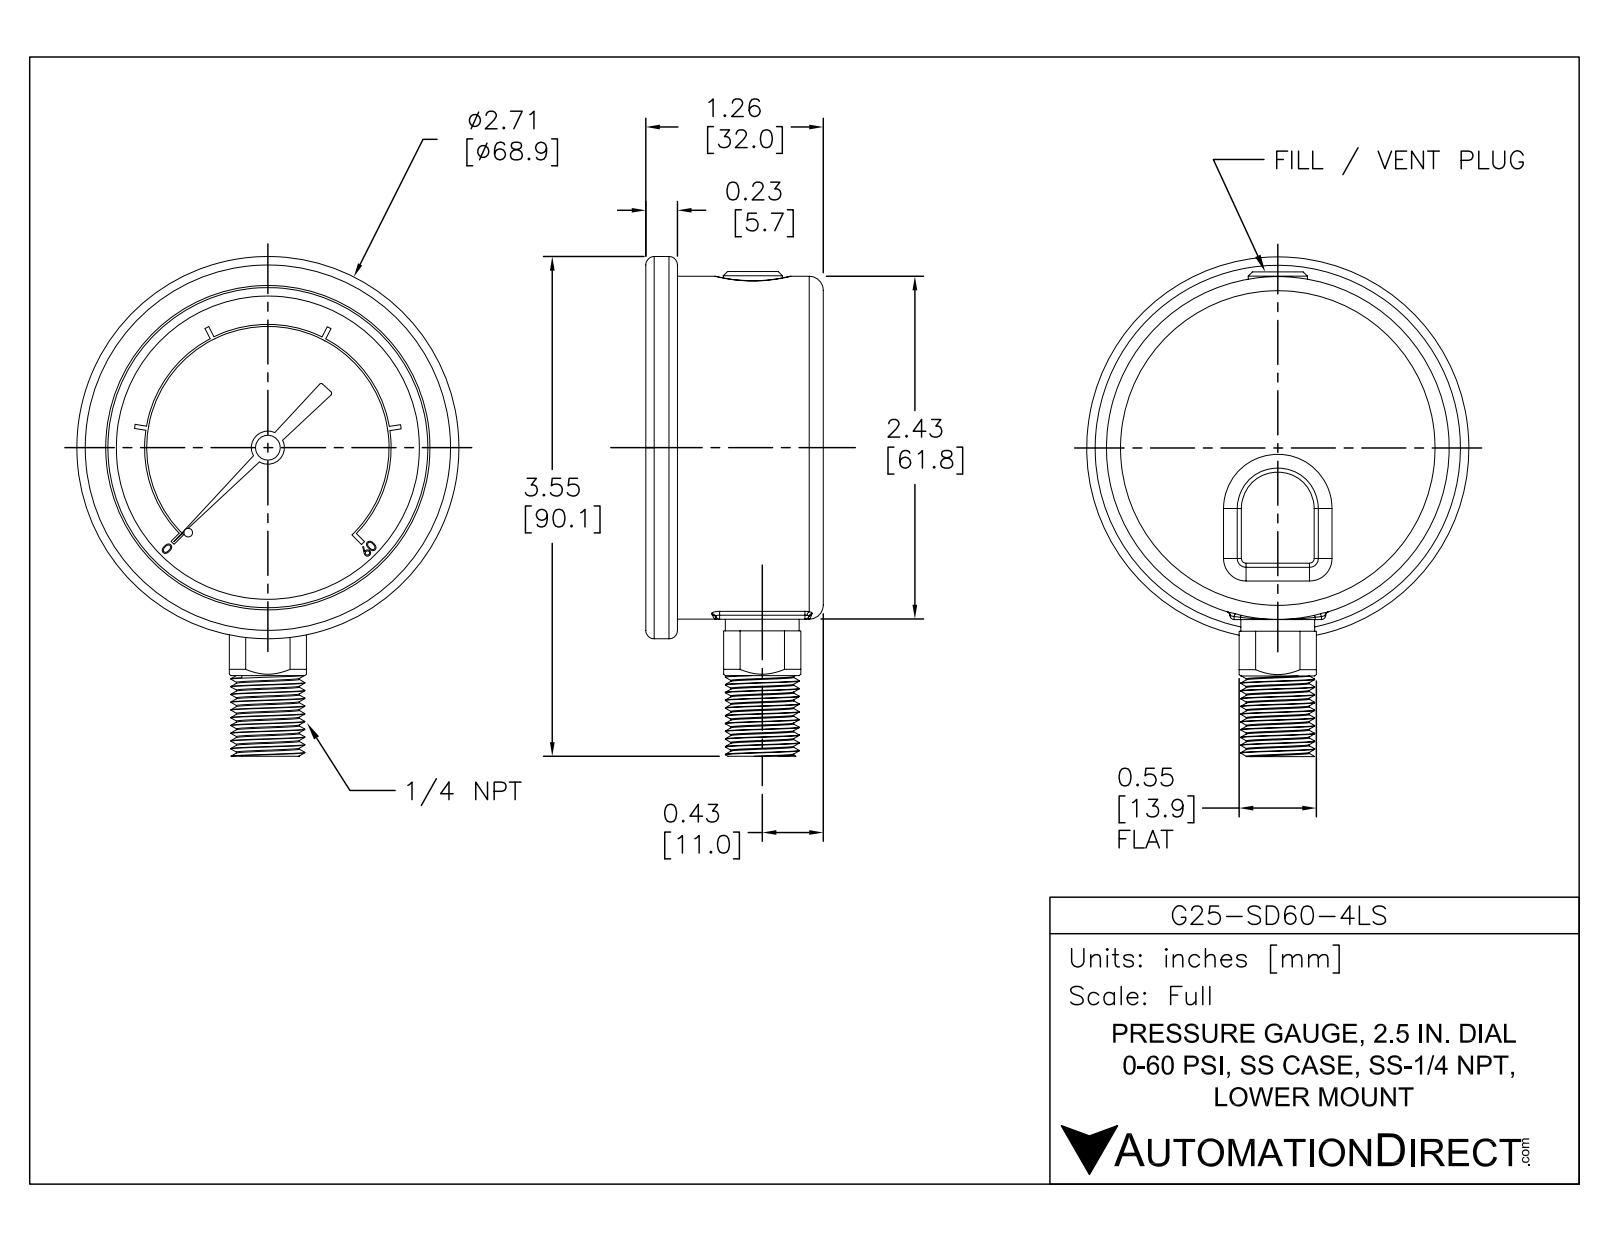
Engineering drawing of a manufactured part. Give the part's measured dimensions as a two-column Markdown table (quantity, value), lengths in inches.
| quantity | value |
| --- | --- |
| part name | G25-SD60-4LS |
| STEP written by | SolidWorks 2021 (AUTOMOTIVE_DESIGN) |
| units | inches |
| bodies | 1 solid, 339 faces (191 planar, 85 cylindrical, 63 other) |
| overall size | 3.546 × 2.713 × 1.26 |
| volume | 5.273 in³ |
| surface area | 24.67 in² |
| round holes (diameter × count) | 0.027 × 1, 0.071 × 1, 0.119 × 1, 2.272 × 1 |
| round bosses / shafts (diameter × count) | 2.713 × 1, 2.433 × 1, 0.524 × 1, 0.42 × 1, 0.235 × 1, 0.176 × 1, 0.14 × 1, 0.041 × 1 |
| partial cylindrical surfaces (radius × count) | 0.03 × 9, 0.1 × 3, 0.015 × 2, 0.316 × 1, 0.86 × 1, 0.875 × 1 |
| main face-to-face distances | 1.01, 1.26, 0.25, 1.035, 0.025, 0.225, 0.1, 0.91, 0.935, 1.16 |
| hole center spacings | 0.067 |
